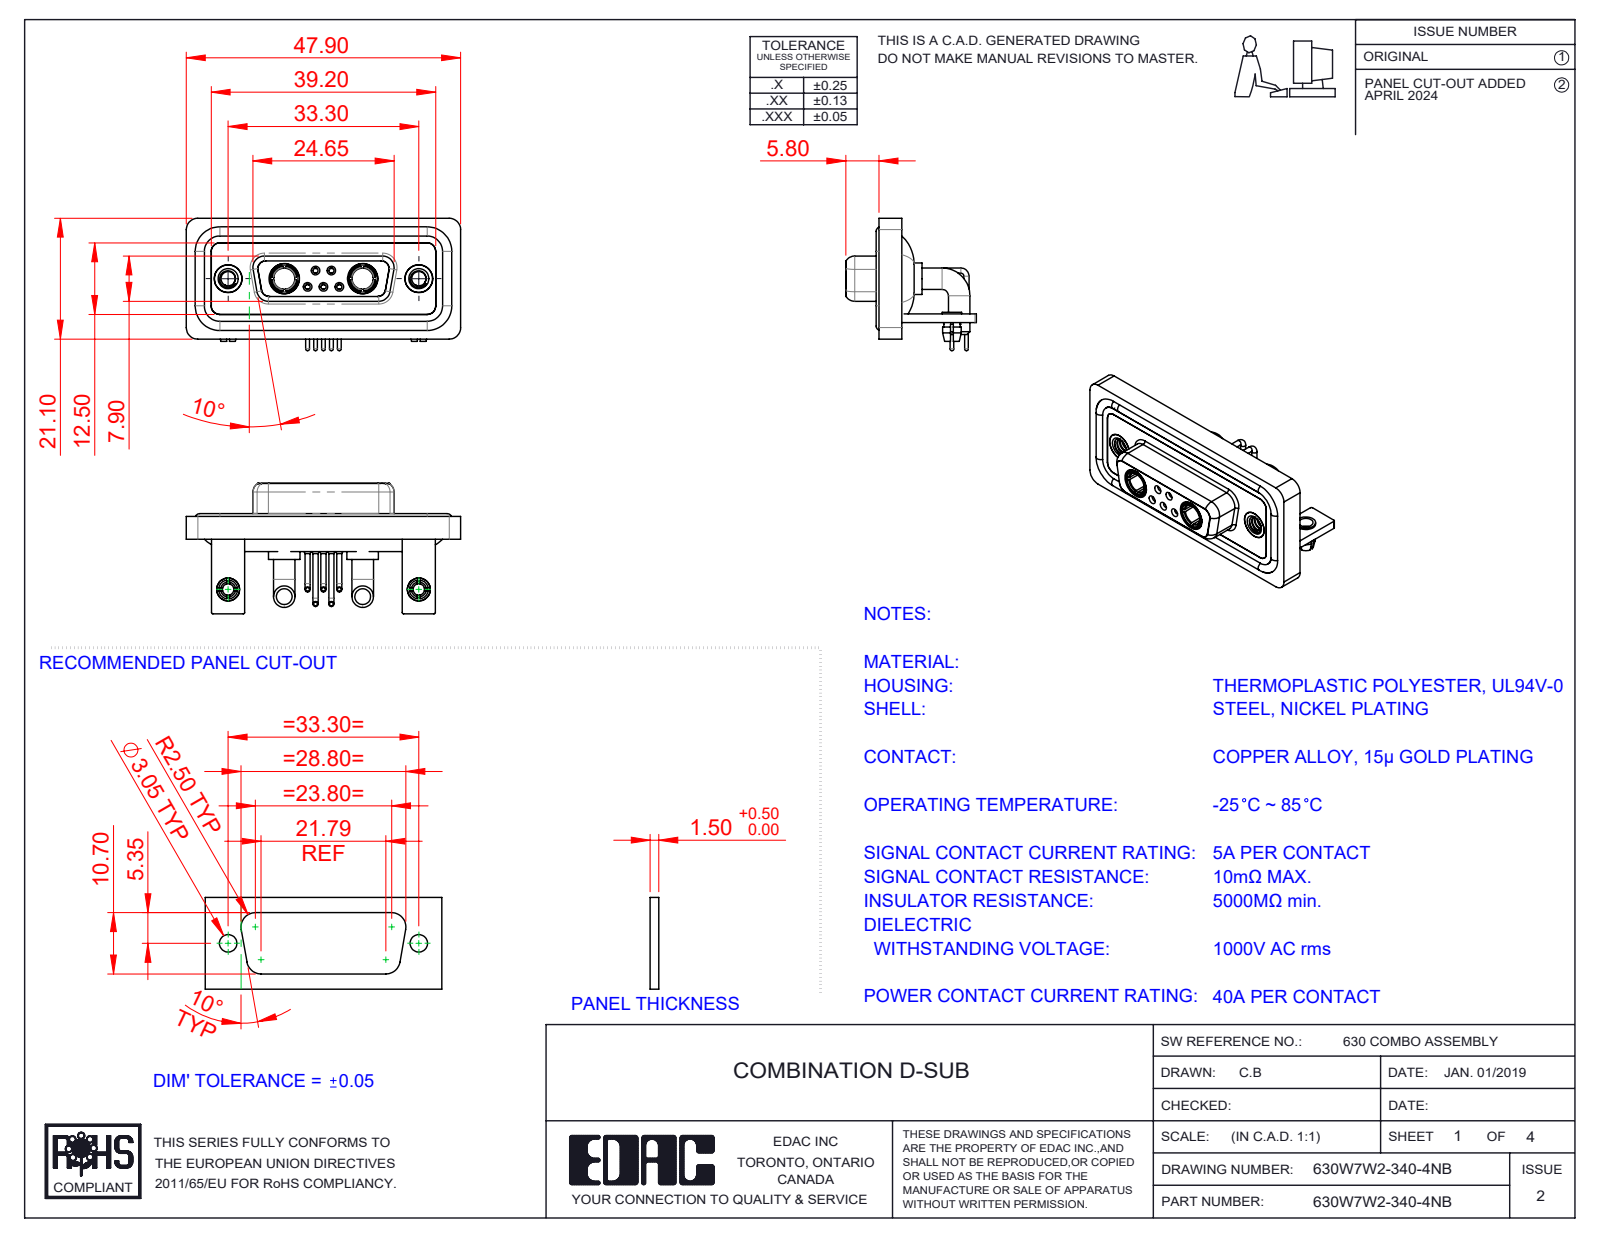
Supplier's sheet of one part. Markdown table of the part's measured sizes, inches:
| quantity | value |
| --- | --- |
| part name | 630Combo Housing_7W2; 630Combo Waterproof Housing_15 Contacts; 630Combo Board Lock_50 Contacts; 630Combo Shell Front_15 Contacts (+7 more) |
| STEP written by | SolidWorks 2023 (CONFIG_CONTROL_DESIGN) |
| units | inches |
| bodies | 20 solids, 941 faces (306 planar, 407 cylindrical, 228 other) |
| overall size | 1.886 × 0.91 × 0.898 |
| volume | 0.411 in³ |
| surface area | 17.43 in² |
| round holes (diameter × count) | 0.079 × 7, 0.035 × 5, 0.043 × 5, 0.059 × 5, 0.098 × 4, 0.191 × 4, 0.063 × 3, 0.067 × 2, 0.126 × 2, 0.146 × 2, 0.157 × 2, 0.159 × 2 |
| round bosses / shafts (diameter × count) | 0.063 × 6, 0.035 × 5, 0.026 × 5, 0.148 × 4, 0.217 × 2, 0.205 × 2, 0.195 × 2, 0.195 × 2 |
| partial cylindrical surfaces (radius × count) | 0.079 × 21, 0.059 × 18, 0.01 × 16, 0.053 × 12, 0.063 × 8, 0.02 × 5, 0.024 × 4, 0.026 × 4 |
| main face-to-face distances | 0.016, 0.114, 0.059, 0.071, 0.146, 0.043, 0.161, 0.063, 0.098, 0.055 |
| hole center spacings | 0.124, 0.109, 0.386, 0.925, 1.311, 0.17, 0.17, 0.198 |
